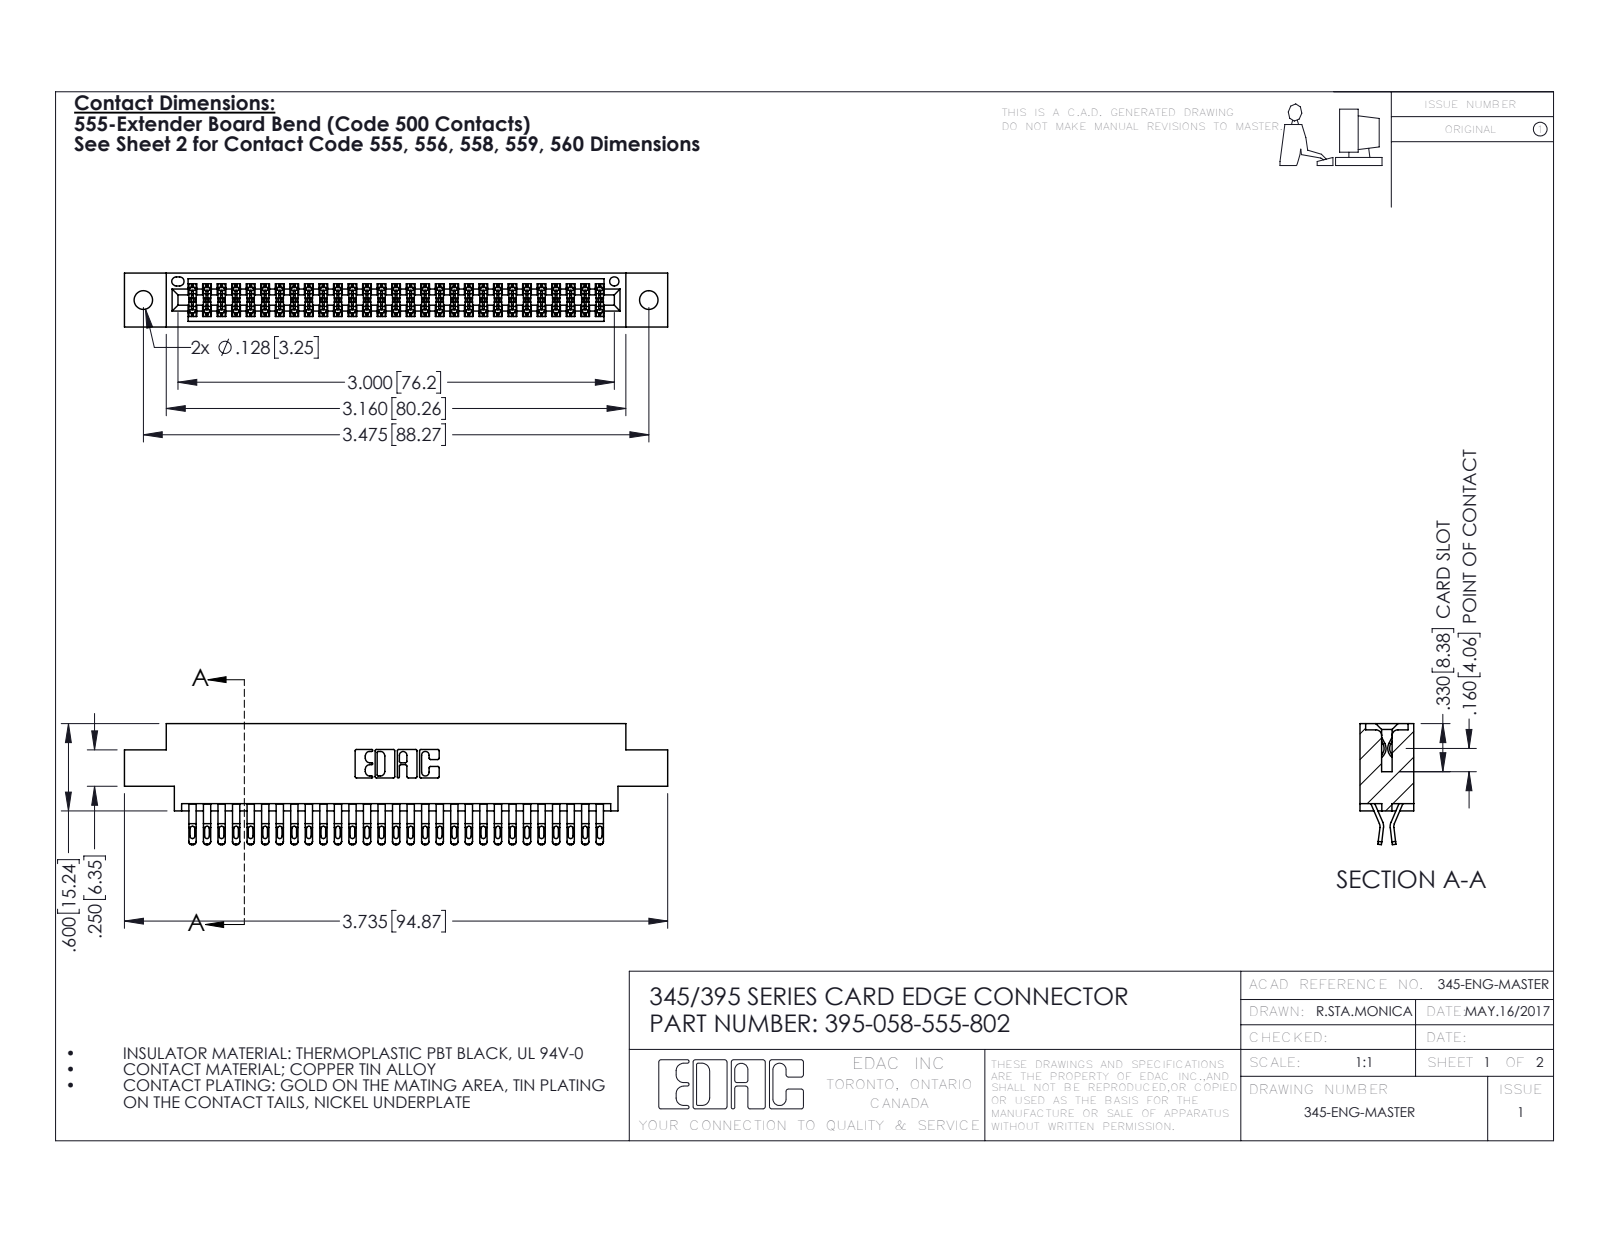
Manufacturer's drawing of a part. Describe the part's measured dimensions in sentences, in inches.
The part is named "395-058-555-802; 345 Part_0.170 Offset - 0.128 Dia; 345-292-001_555 Tail". Its 3-D file was written by "SolidWorks 2016 (CONFIG_CONTROL_DESIGN)". It is 59 solids with 3378 faces: 1882 planar, 1496 cylindrical and 0 other. Overall it measures 3.735 by 0.832 by 0.37 inches. Its volume is 0.556 cubic inches and its surface area 21.2 square inches. Round holes: 2 of diameter 0.128, 1 of diameter 0.064. Partial cylindrical surfaces (rounded edges, fillets, slot ends): 145 of radius 0.016, 116 of radius 0.02, 87 of radius 0.006, 22 of radius 0.01, 6 of radius 0.007, 6 of radius 0.031, 3 of radius 0.026, 2 of radius 0.01. The main face-to-face distances are 0.298, 0.072, 0.37, 0.025, 0.2, 0.098, 0.272, 0.225, 0.175, 0.149. The hole center spacings are 0.27, 3.24, 3.475.
